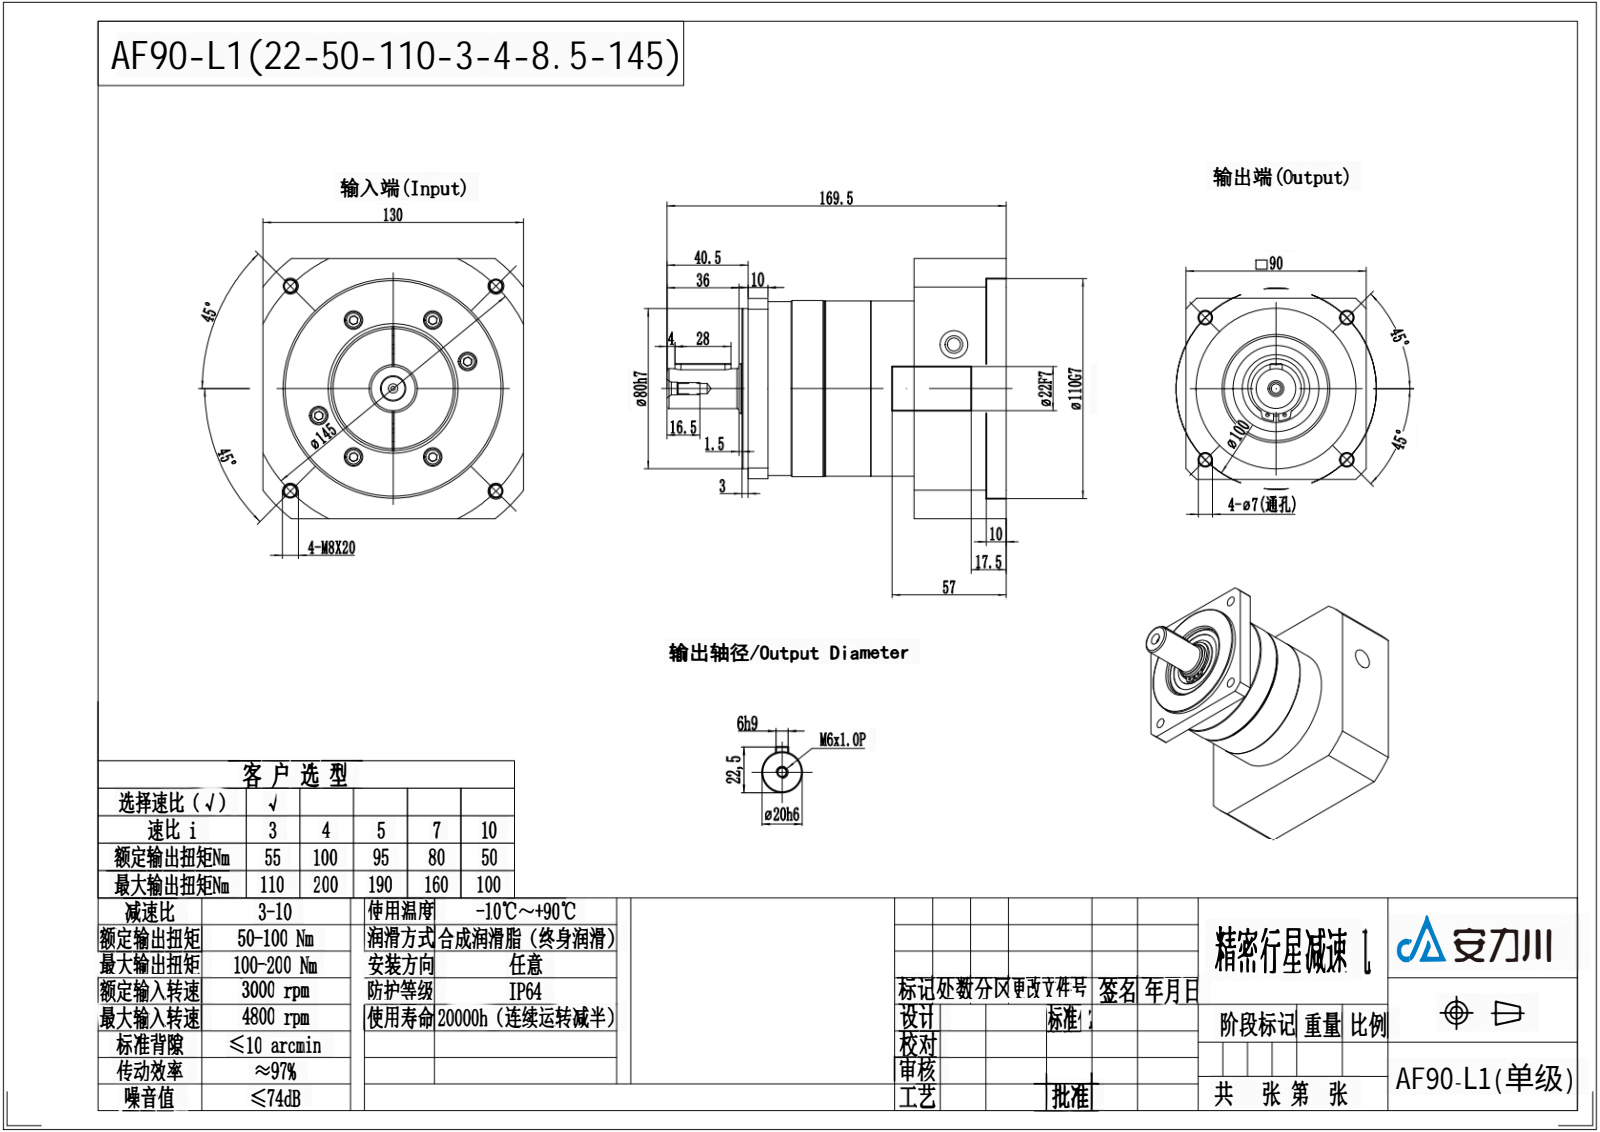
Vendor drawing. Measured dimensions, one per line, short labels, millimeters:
name: circlips for shaft--type a large gb_GB_CONNECTING_PIECE_RING_RRA 25_1; MYF090-L1-22-110-145-M8-57; 090输出轴-20_1; 6205-2rz_1 (+8 more)
written by: SolidWorks 2014 (AUTOMOTIVE_DESIGN)
unit: mm
bodies: 21 solids, 868 faces (221 planar, 299 cylindrical, 348 other)
size: 169.5 × 130 × 130
volume: 852 336 mm³; area: 207 732 mm²
holes: 6× ⌀4.2, 6× ⌀5.4, 6× ⌀5.5, 6× ⌀6.8, 6× ⌀9.5, 4× ⌀7, 3× ⌀6, 2× ⌀2, 2× ⌀9, 2× ⌀14, 1× ⌀2.5, 1× ⌀5
bosses: 6× ⌀8.5, 6× ⌀8, 6× ⌀5, 1× ⌀88, 1× ⌀87.5, 1× ⌀87, 1× ⌀80, 1× ⌀62
rounds: 2× R0.5, 2× R1, 2× R2.5, 2× R3, 1× R60, 1× R82.5
face distances: 130, 46, 33.5, 16.5, 44.5, 20, 41.5, 64.5, 12, 34
hole spacings: 39.5, 88.07, 22.5, 70.71, 102.53, 122.5, 25.45, 44.08
